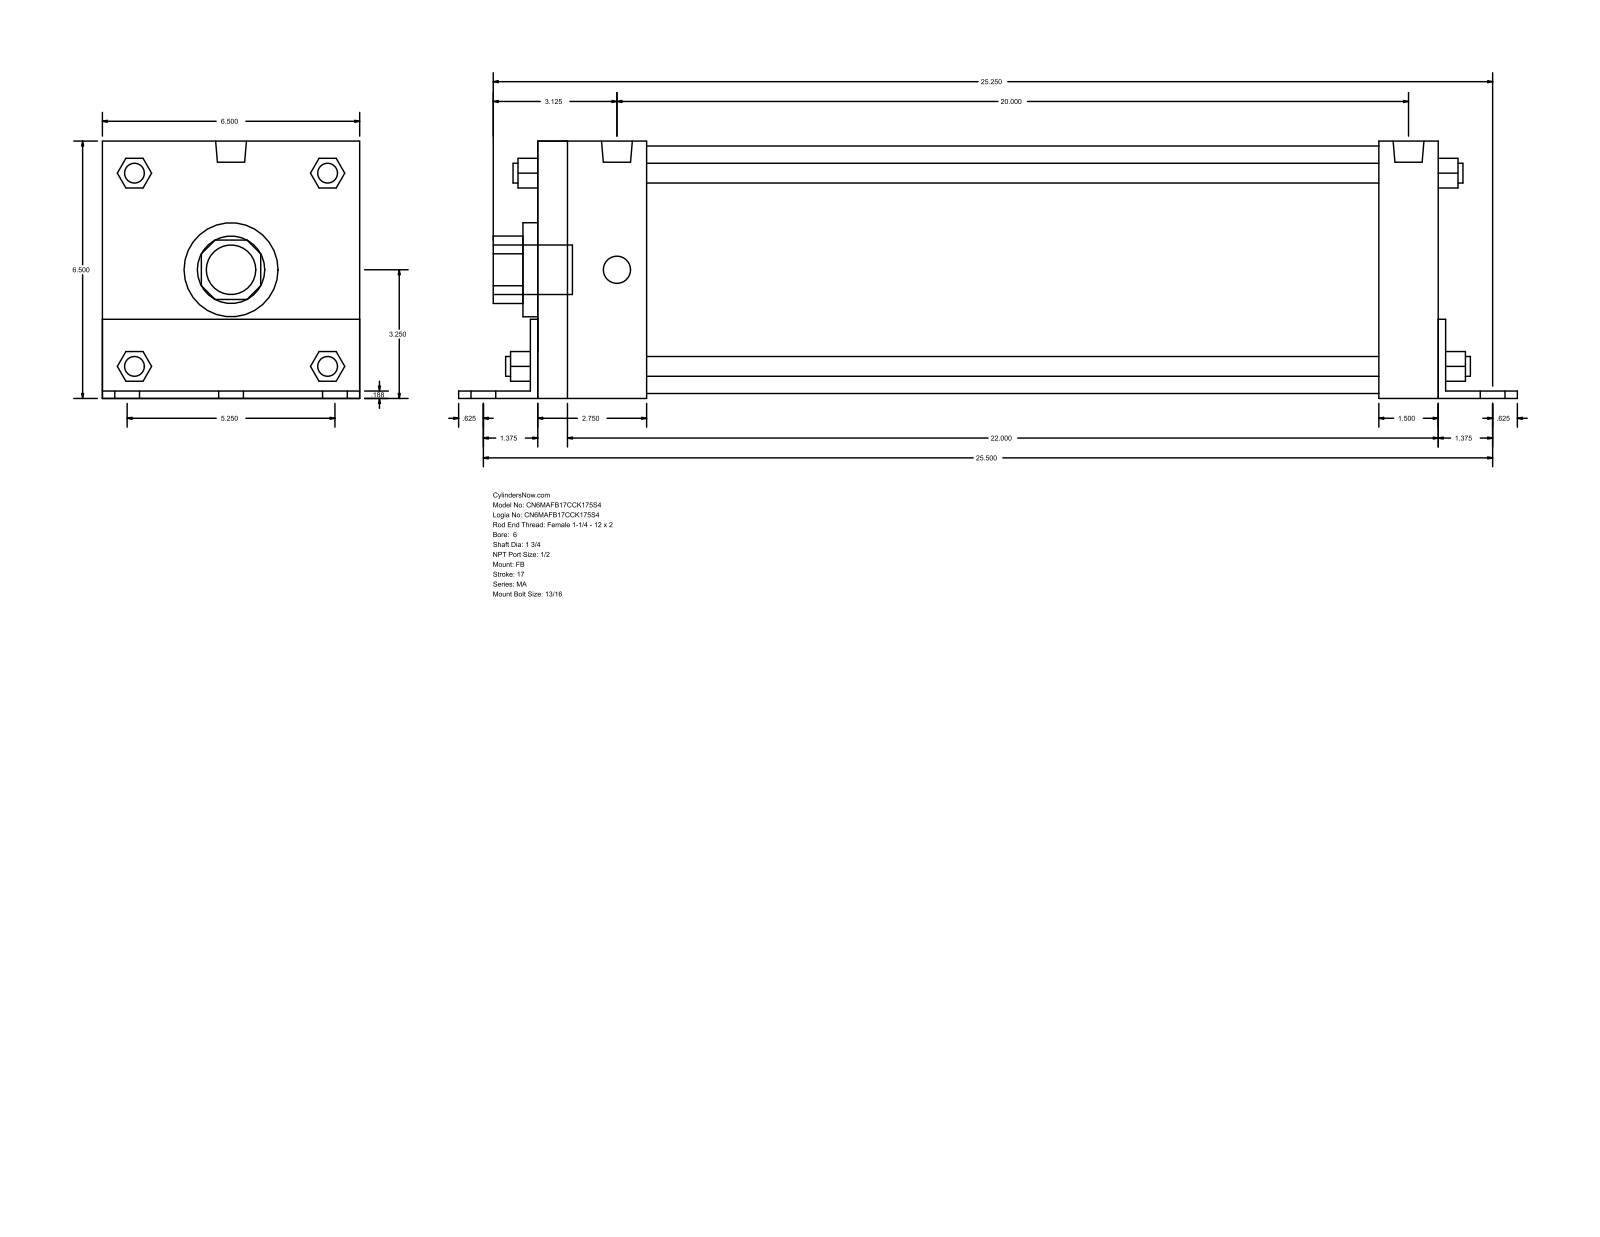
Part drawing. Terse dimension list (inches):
name: MA_FB__0600_1.75
written by: GSSL Pune (CONFIG_CONTROL_DESIGN)
unit: in
bodies: 0 solids, 140 faces (105 planar, 35 cylindrical, 0 other)
size: 26.75 × 6.502 × 6.5
holes: 1× ⌀1.75, 1× ⌀2.375, 1× ⌀6.25
bosses: 6× ⌀0.813, 4× ⌀0.687, 4× ⌀0.5, 2× ⌀0.778, 1× ⌀1.25
rounds: 1× R0.852, 1× R1.262
face distances: 6.5, 0.187, 22.75, 6.502, 0.185, 6.315, 0.188, 1.687, 22.938, 22.937
